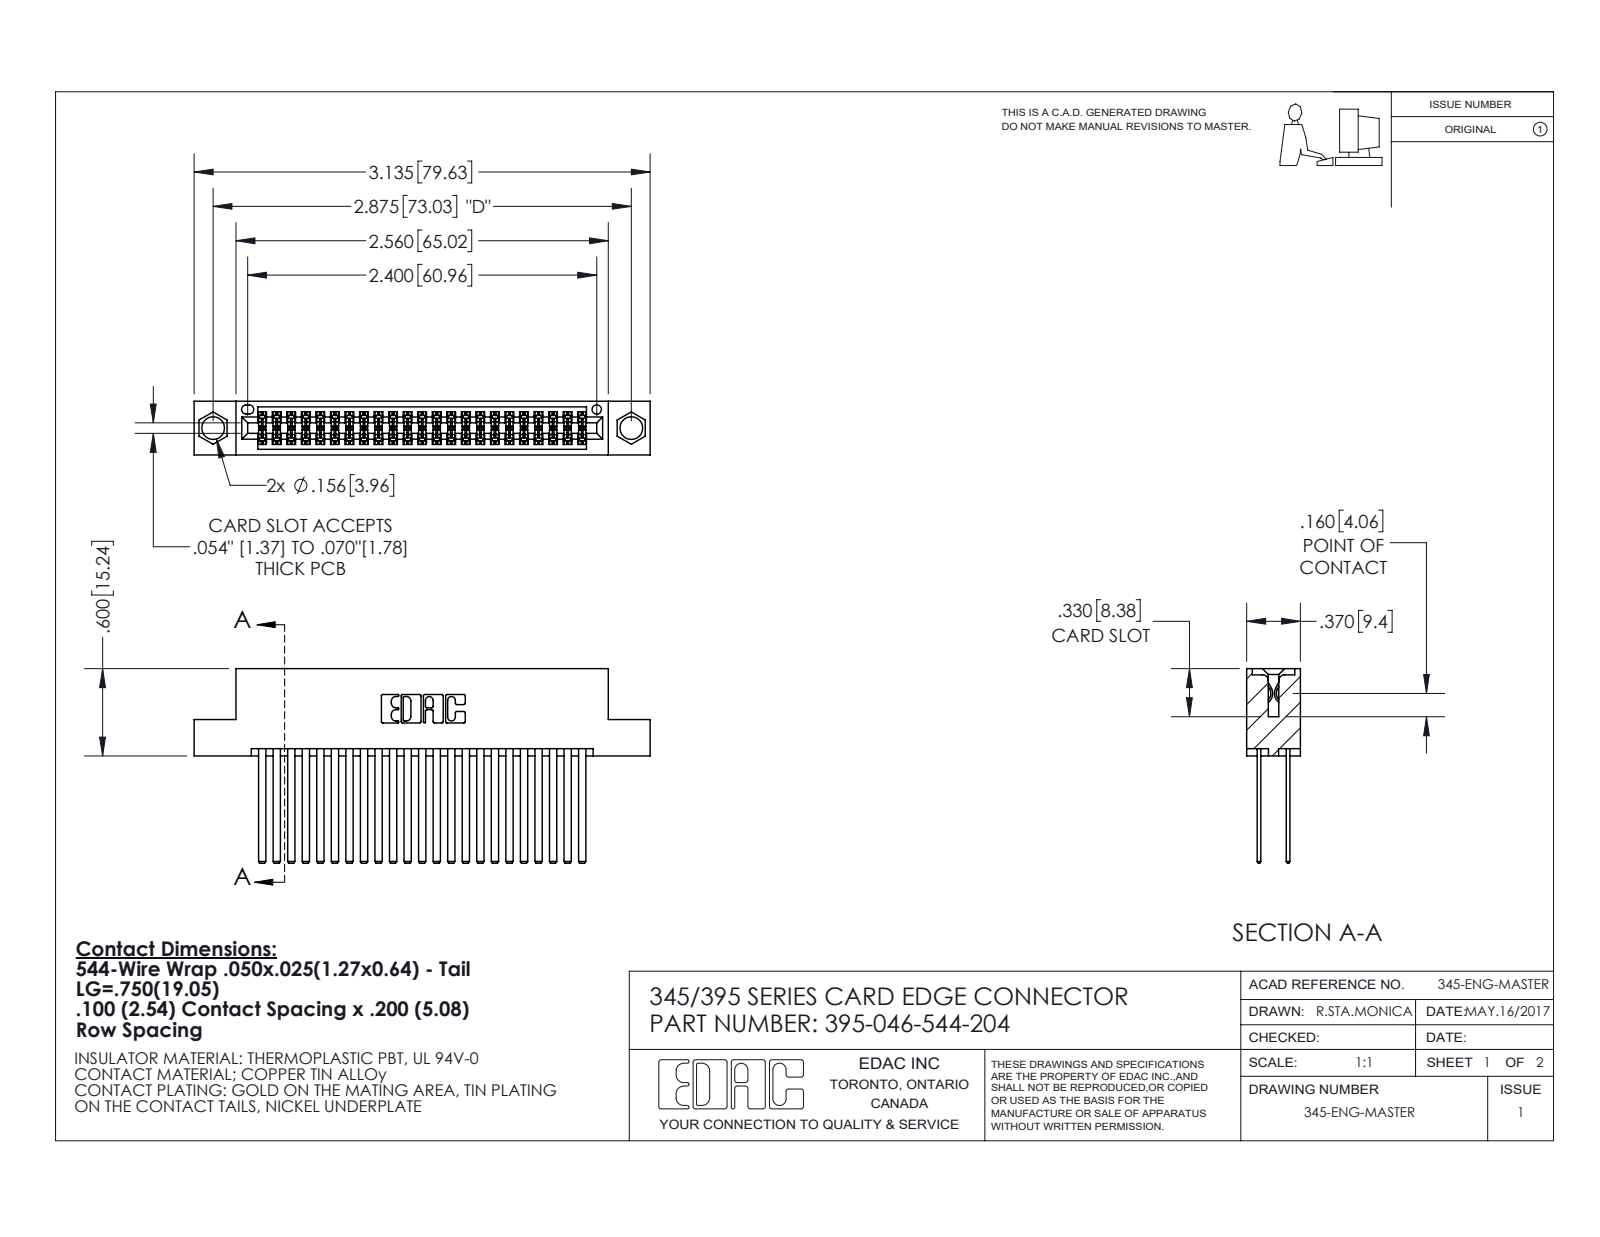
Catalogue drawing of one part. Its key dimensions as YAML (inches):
part_name: "345 Part_Flush Mounting Lugs - 0.156 Dia-TI; 345-292-001_345-293-144; 395-046-544-204"
step_written_by: "SolidWorks 2020 (CONFIG_CONTROL_DESIGN)"
units: inches
bodies: {solids: 47, faces: 2164, planar: 1428, cylindrical: 736, other: 0}
overall_size: [3.135, 1.337, 0.37]
volume: 0.494
surface_area: 20.68
round_holes:
  - {diameter: 0.156, count: 2}
  - {diameter: 0.064, count: 1}
partial_cylinders:
  - {radius: 0.006, count: 92}
  - {radius: 0.01, count: 22}
  - {radius: 0.007, count: 6}
  - {radius: 0.031, count: 6}
  - {radius: 0.026, count: 3}
  - {radius: 0.014, count: 2}
  - {radius: 0.019, count: 2}
  - {radius: 0.022, count: 2}
face_to_face_distances: [0.2, 0.072, 0.298, 0.098, 0.272, 0.025, 0.225, 0.37, 0.175, 0.05]
hole_center_spacings: [0.27, 2.641, 2.875]
